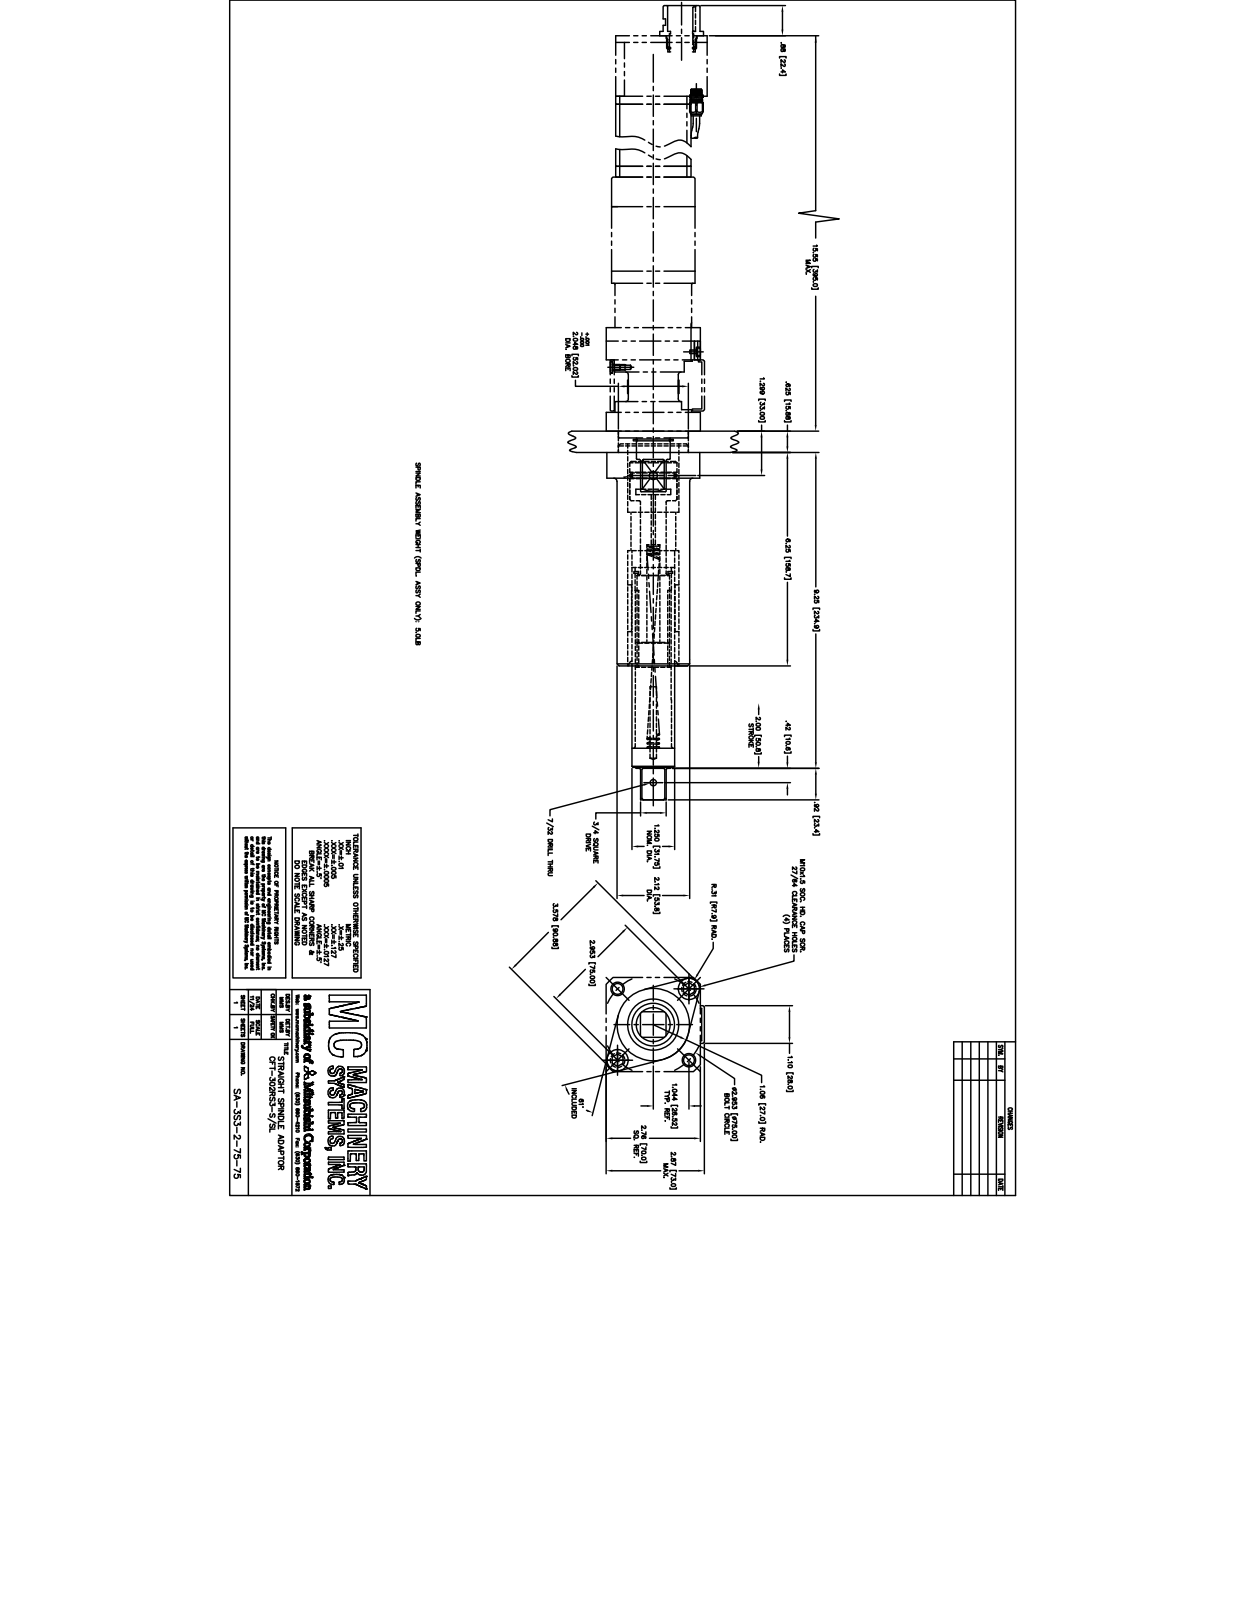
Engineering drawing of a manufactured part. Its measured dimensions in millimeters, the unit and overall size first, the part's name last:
Units: millimetres
Overall size (bounding box): 264.67 × 90.93 × 53.98
Round holes (diameter × count): ⌀5.56 ×2, ⌀10.72 ×2, ⌀3.18 ×1, ⌀9.53 ×1, ⌀24.13 ×1, ⌀25.4 ×1, ⌀25.91 ×1, ⌀26.97 ×1, ⌀28.7 ×1, ⌀31.75 ×1, ⌀32.54 ×1
Round bosses / shafts (diameter × count): ⌀53.97 ×1, ⌀51.99 ×1, ⌀38.1 ×1, ⌀34.92 ×1, ⌀19.05 ×1
Partial cylindrical surfaces — rounded edges, fillets, slot ends (radius × count): R7.94 ×2
Main face-to-face distances: 25.4, 19.17, 60.33, 139.7, 79.37, 158.75, 6.35, 165.1, 19.05, 41.65
Hole centre spacings: 37.5, 75
Volume: 353 665 mm³ · Surface area: 119 657 mm²
Bodies: 6 solids, 138 faces (50 planar, 66 cylindrical, 22 other)
Part name (STEP PRODUCT): SA-3S3-2-75-75; R-7-12-6.78-20-1; SA-003; SA-355H-B
STEP written by: SolidWorks 2013 (CONFIG_CONTROL_DESIGN)
